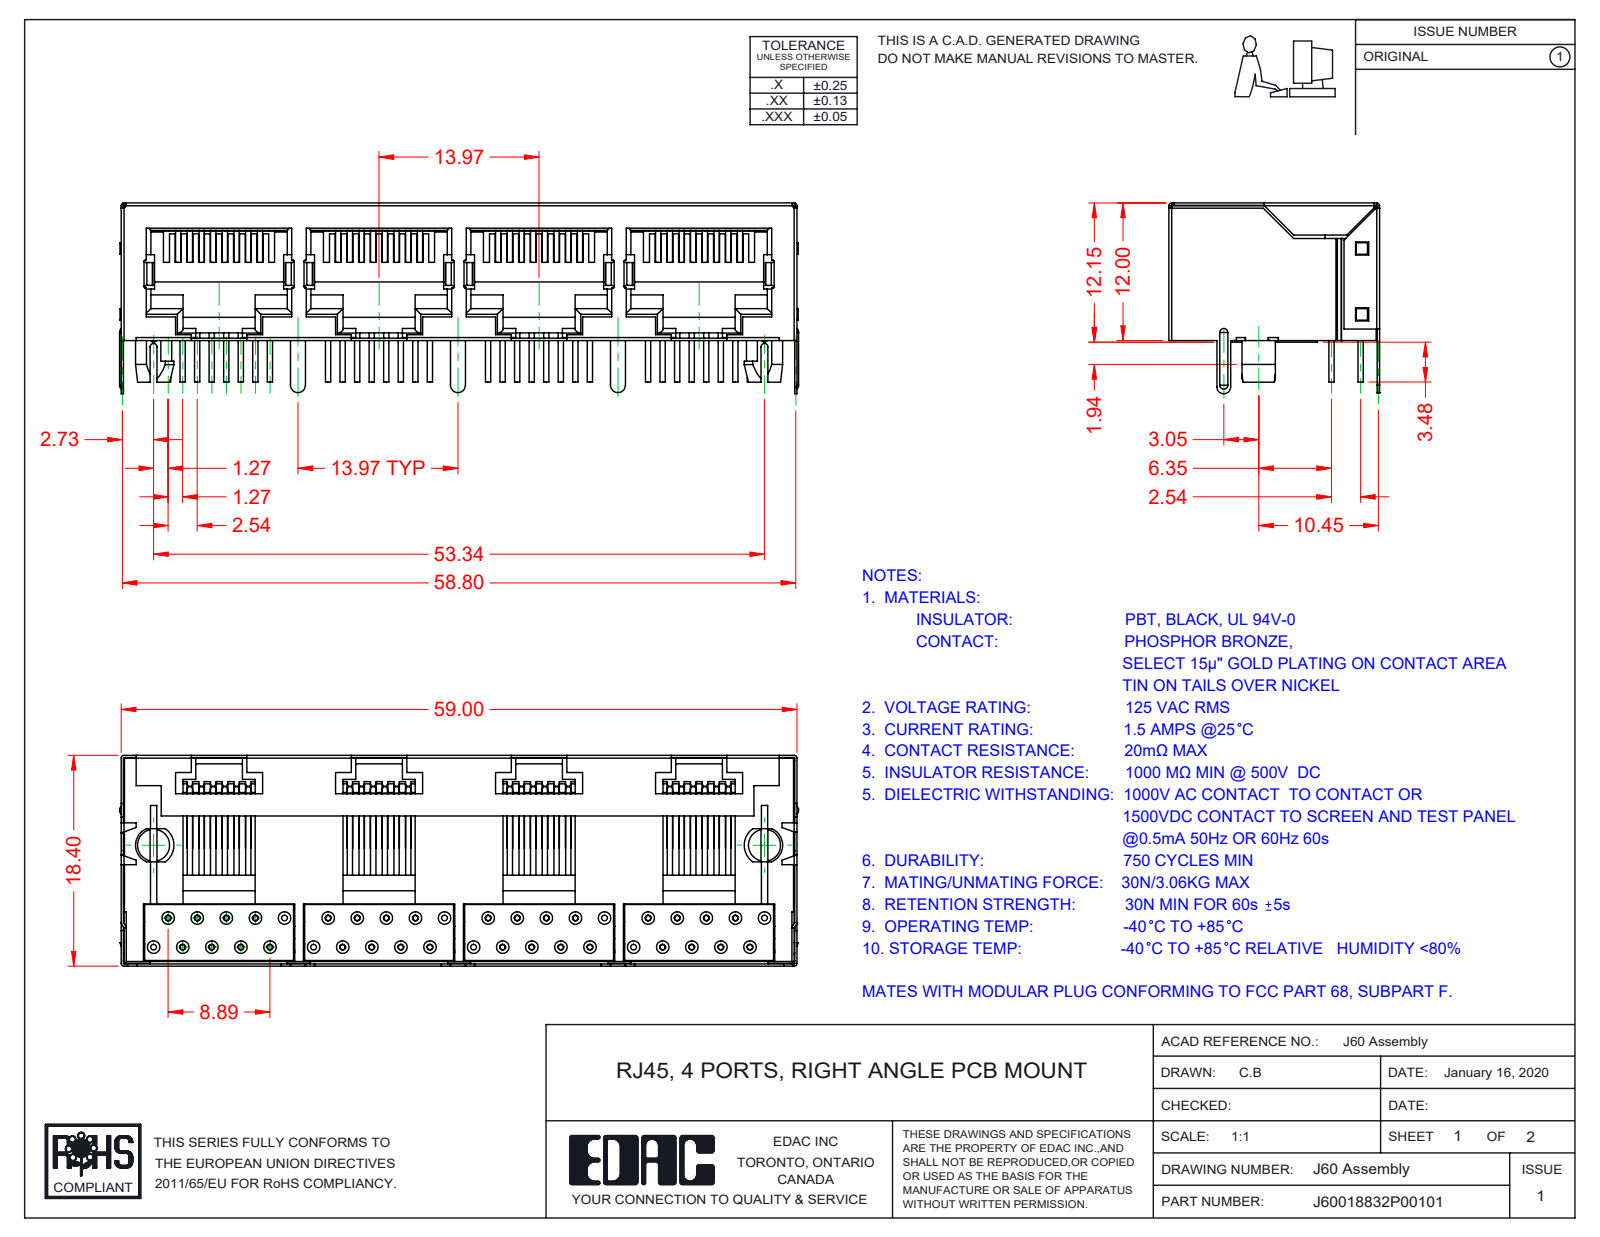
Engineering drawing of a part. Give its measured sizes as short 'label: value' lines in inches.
name: 60 Contacts_8P8C; 60 Shield; 60 Insulator; RJ60048832P00101
written by: SolidWorks 2016 (CONFIG_CONTROL_DESIGN)
unit: in
bodies: 34 solids, 2562 faces (1489 planar, 715 cylindrical, 358 other)
size: 2.335 × 0.724 × 0.656
volume: 0.428 in³; area: 28.77 in²
holes: 40× ⌀0.02, 40× ⌀0.043
bosses: 96× ⌀0.018
rounds: 26× R0.012, 21× R0.01, 18× R0.02, 16× R0.004, 10× R0.008, 7× R0.031, 3× R0.026, 2× R0.011
face distances: 0.02, 0.463, 0.455, 0.55, 0.086, 0.212, 0.204, 0.192, 0.717, 0.453
hole spacings: 0.112, 0.1, 0.18, 0.55, 0.2, 0.51, 0.608, 0.45
